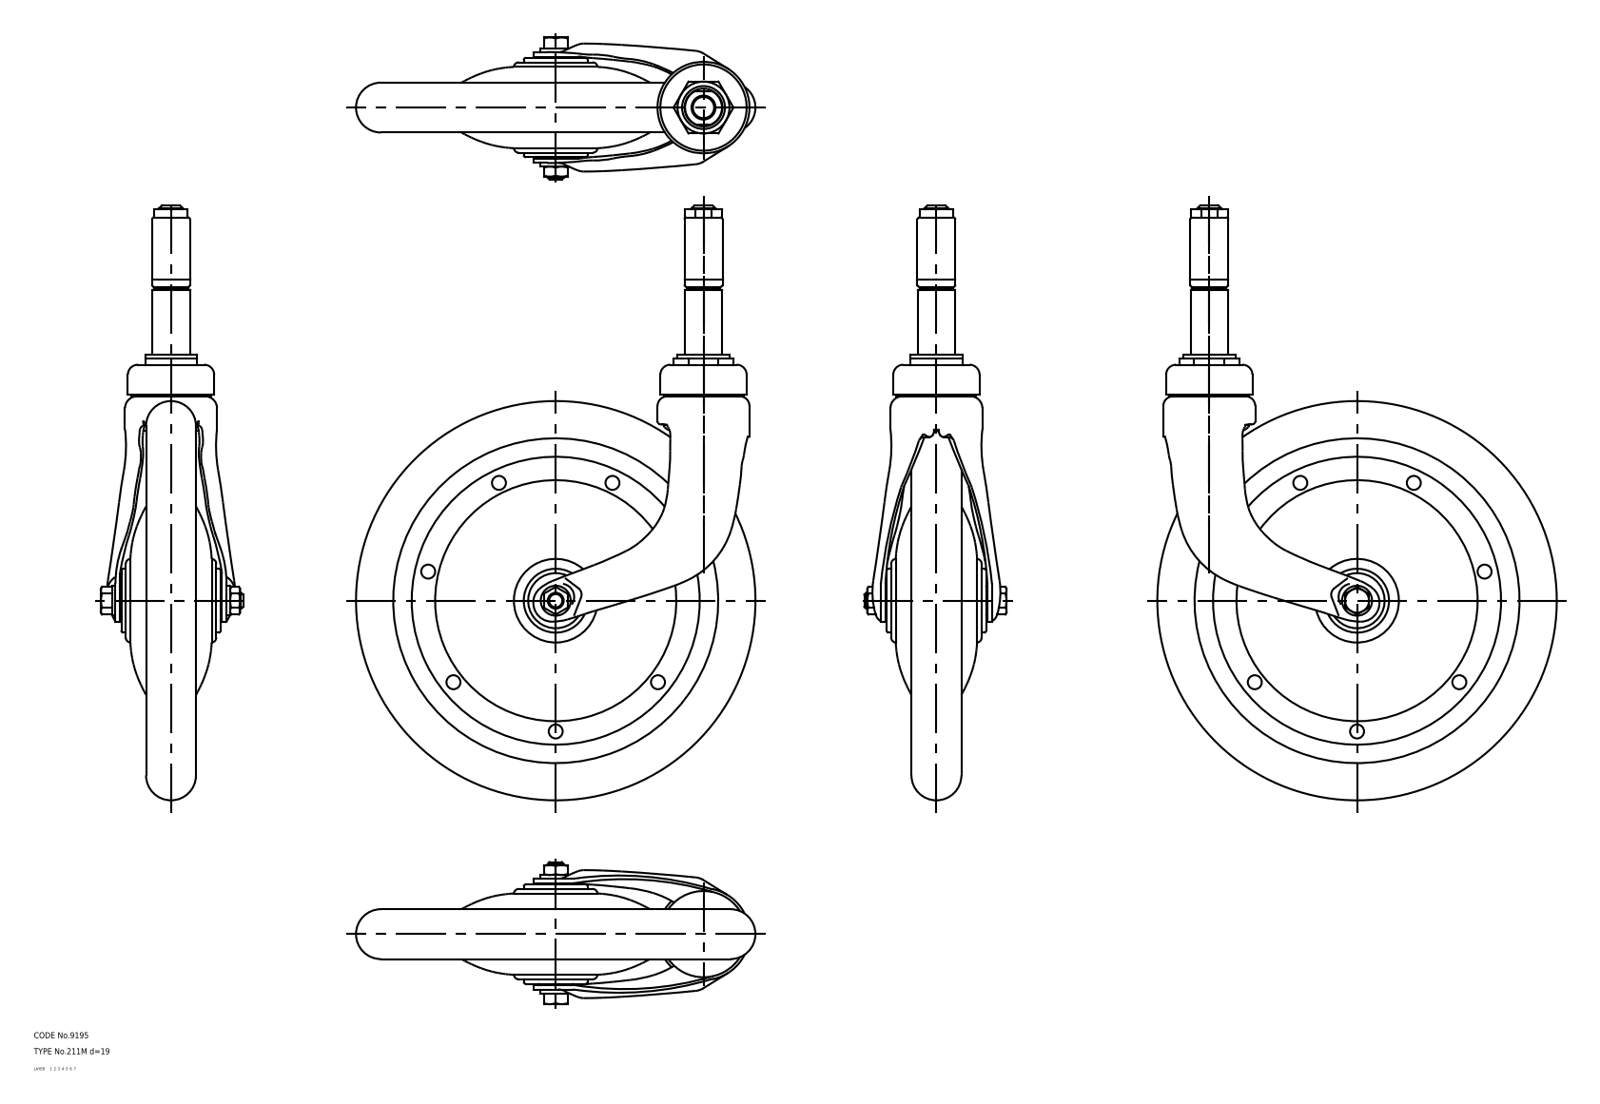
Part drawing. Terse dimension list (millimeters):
name: 67135300; 67135313; 67135326; 67135339
written by: CADfix (AUTOMOTIVE_DESIGN)
unit: mm
bodies: 4 solids, 364 faces (0 planar, 0 cylindrical, 364 other)
size: 298 × 200 × 71.2
volume: 760 419 mm³; area: 128 117 mm²
